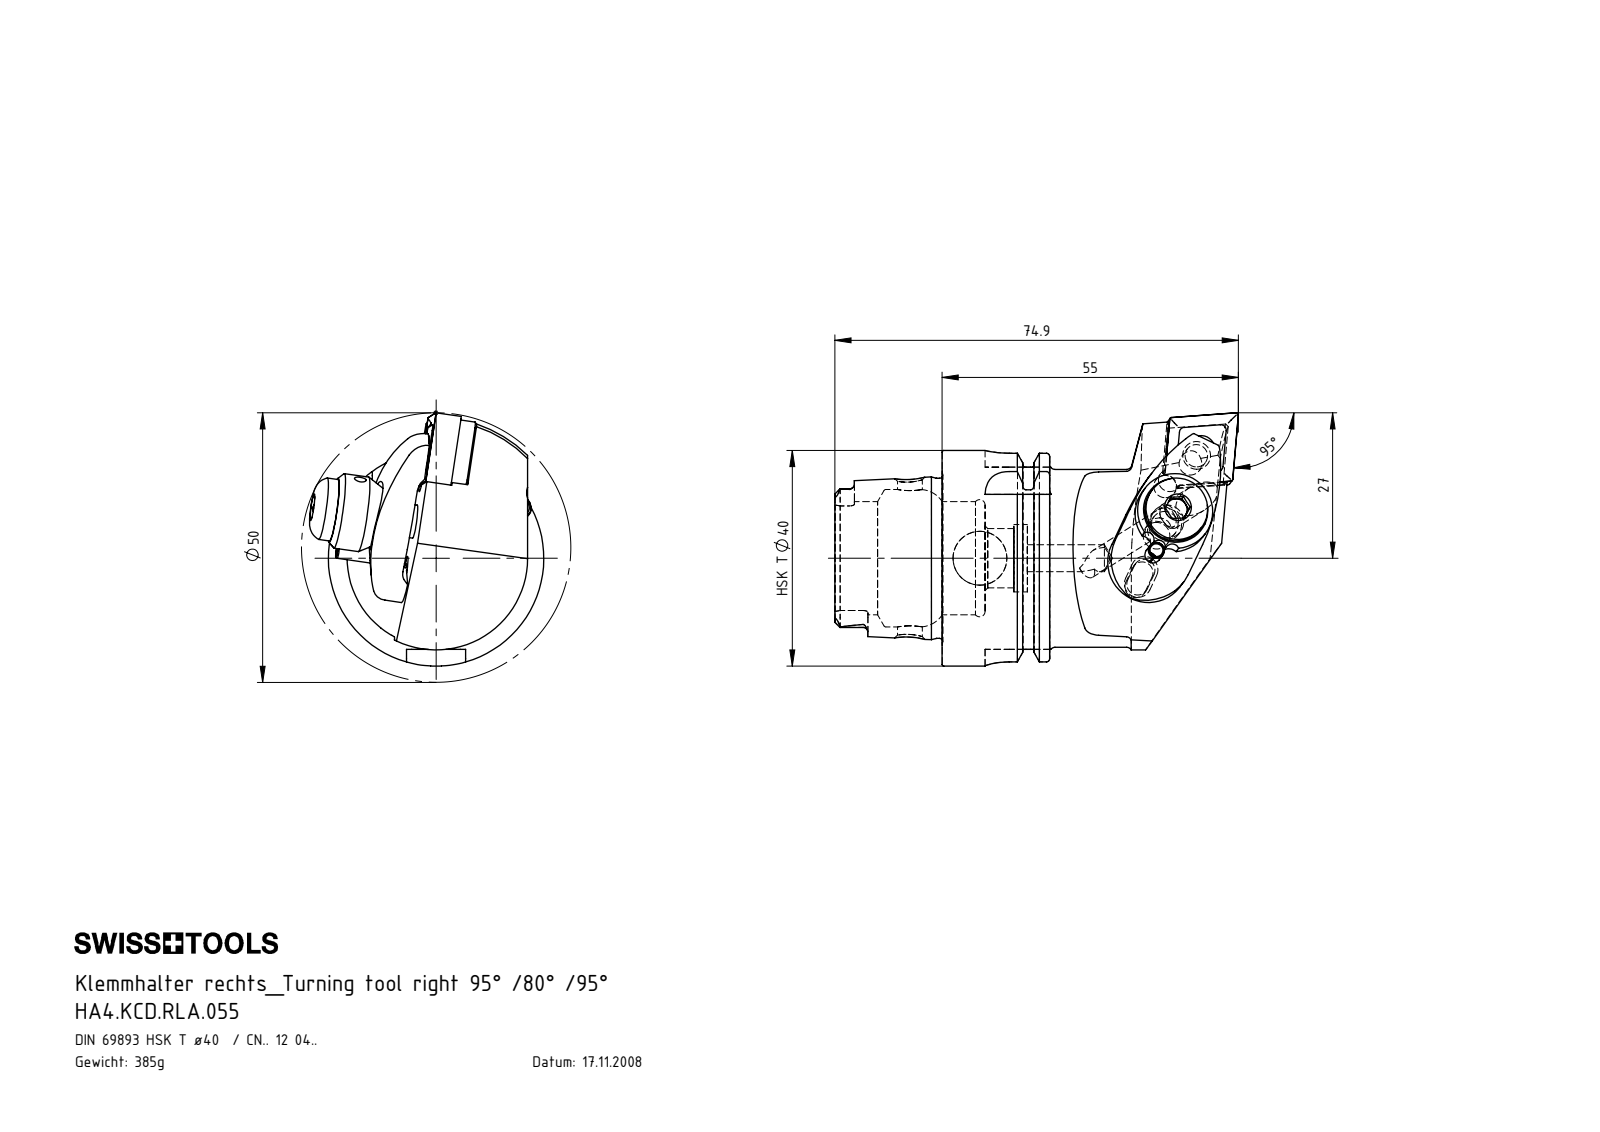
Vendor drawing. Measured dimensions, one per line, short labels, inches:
name: HA4.KCD.RLA.055; ISO 13337 - 3 x 12_PreviewCfg; WCC-ER3.102.024_C; CNMG120404 (+7 more)
written by: SolidWorks 2017 (CONFIG_CONTROL_DESIGN)
unit: in
bodies: 11 solids, 471 faces (124 planar, 155 cylindrical, 192 other)
size: 2.949 × 1.85 × 1.668
volume: 2.945 in³; area: 29.13 in²
holes: 3× ⌀0.079, 3× ⌀0.165, 3× ⌀0.197, 2× ⌀0.276, 1× ⌀0.094, 1× ⌀0.118, 1× ⌀0.157, 1× ⌀0.181, 1× ⌀0.203, 1× ⌀0.244, 1× ⌀0.252, 1× ⌀0.335
bosses: 2× ⌀0.197, 2× ⌀0.118, 1× ⌀1.575, 1× ⌀1.368, 1× ⌀1.299, 1× ⌀1.17, 1× ⌀0.551, 1× ⌀0.453
rounds: 6× R0.015, 6× R0.035, 4× R0.016, 4× R0.039, 4× R0.177, 3× R0.027, 3× R0.027, 3× R0.059
face distances: 0.313, 0.177, 0.227, 0.05, 0.126, 0.302, 0.352, 0.785, 0.472, 0.783
hole spacings: 0.315, 0.588, 0.903, 0.591, 0.608, 0.906, 0.296, 0.304
